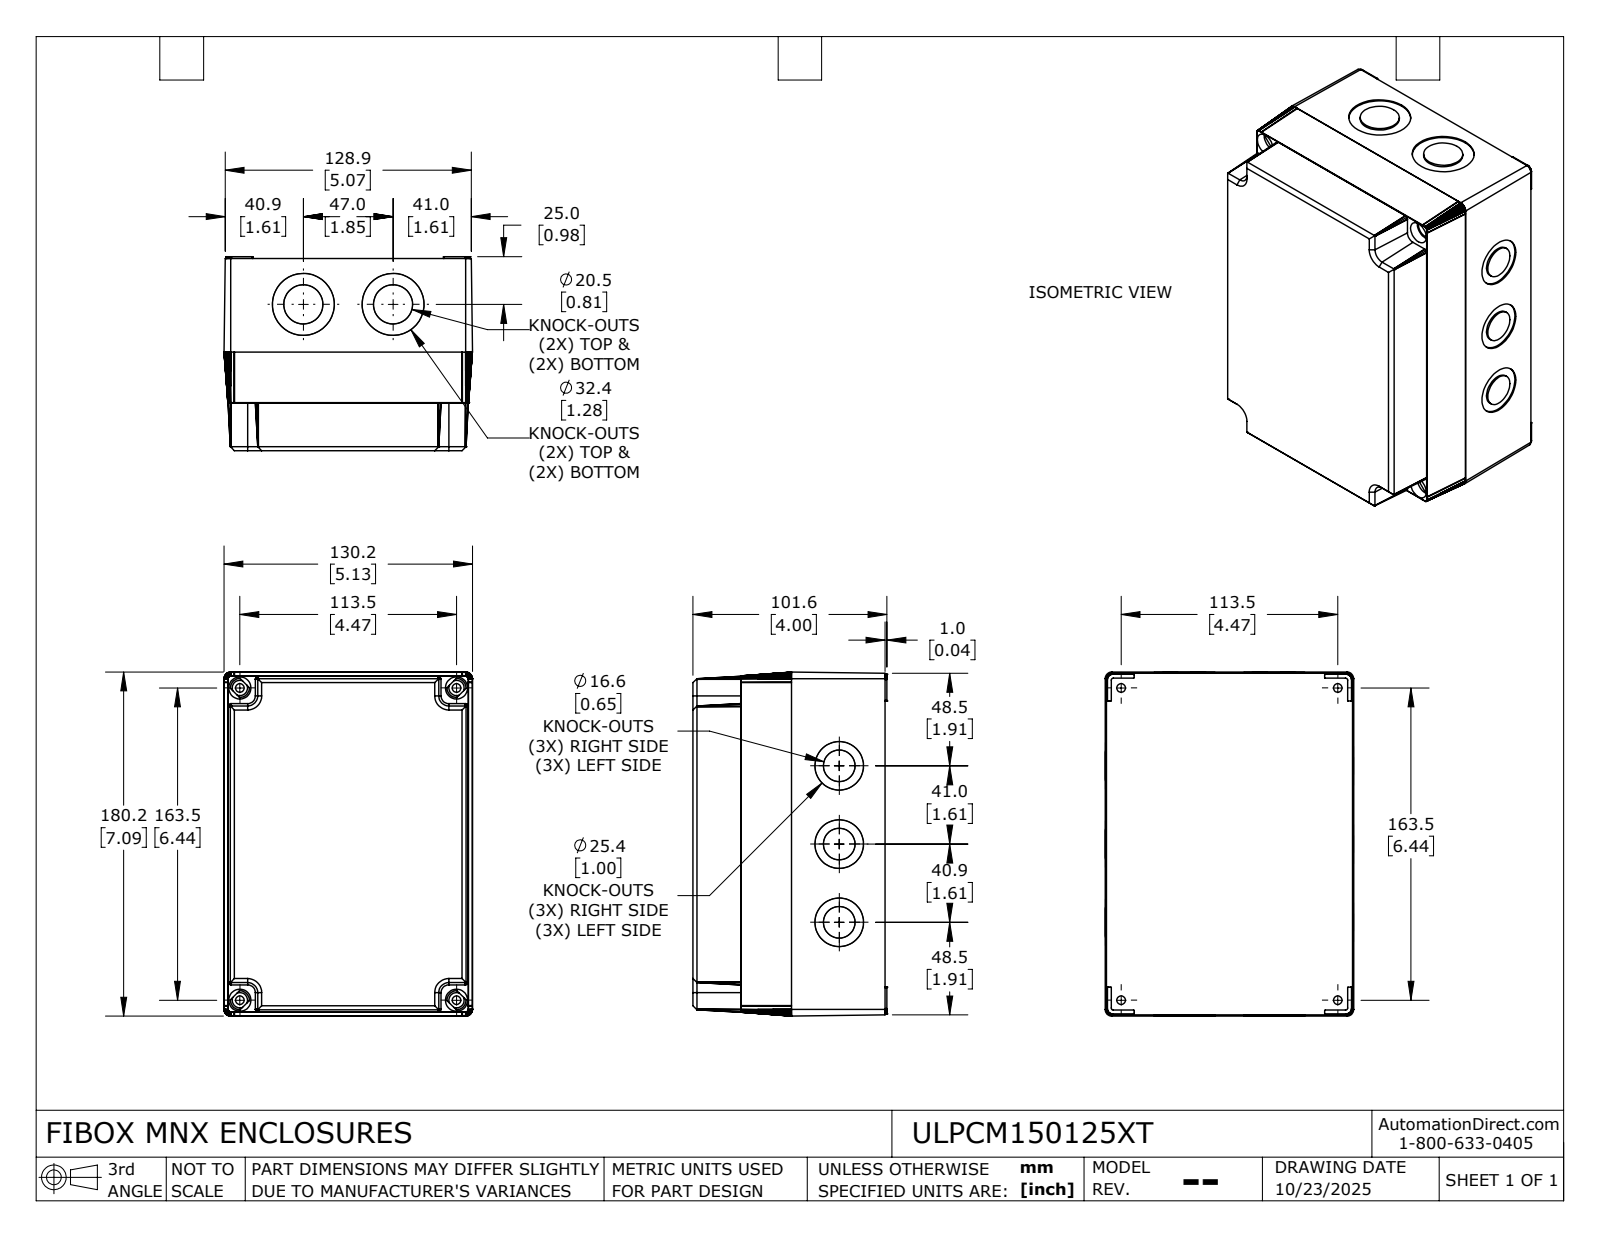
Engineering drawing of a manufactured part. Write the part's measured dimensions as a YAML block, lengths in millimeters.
part_name: "ULPCM20088XT"
step_written_by: "SolidWorks 2024 (AUTOMOTIVE_DESIGN)"
units: millimeters
bodies: {solids: 2, faces: 1665, planar: 1517, cylindrical: 60, other: 88}
overall_size: [180.18, 130.18, 101.6]
volume: 326687
surface_area: 217660
round_holes:
  - {diameter: 4.5, count: 4}
  - {diameter: 8, count: 4}
  - {diameter: 11.59, count: 4}
partial_cylinders:
  - {radius: 4.02, count: 8}
  - {radius: 4.86, count: 8}
  - {radius: 0.26, count: 4}
  - {radius: 1.1, count: 4}
  - {radius: 1.9, count: 4}
  - {radius: 2.9, count: 4}
  - {radius: 4.96, count: 4}
  - {radius: 5.1, count: 4}
face_to_face_distances: [3.46, 3, 100.6, 97.6, 2, 98.6, 95.6, 2.44, 49, 46]
hole_center_spacings: [113.5, 163.5, 199.03]
